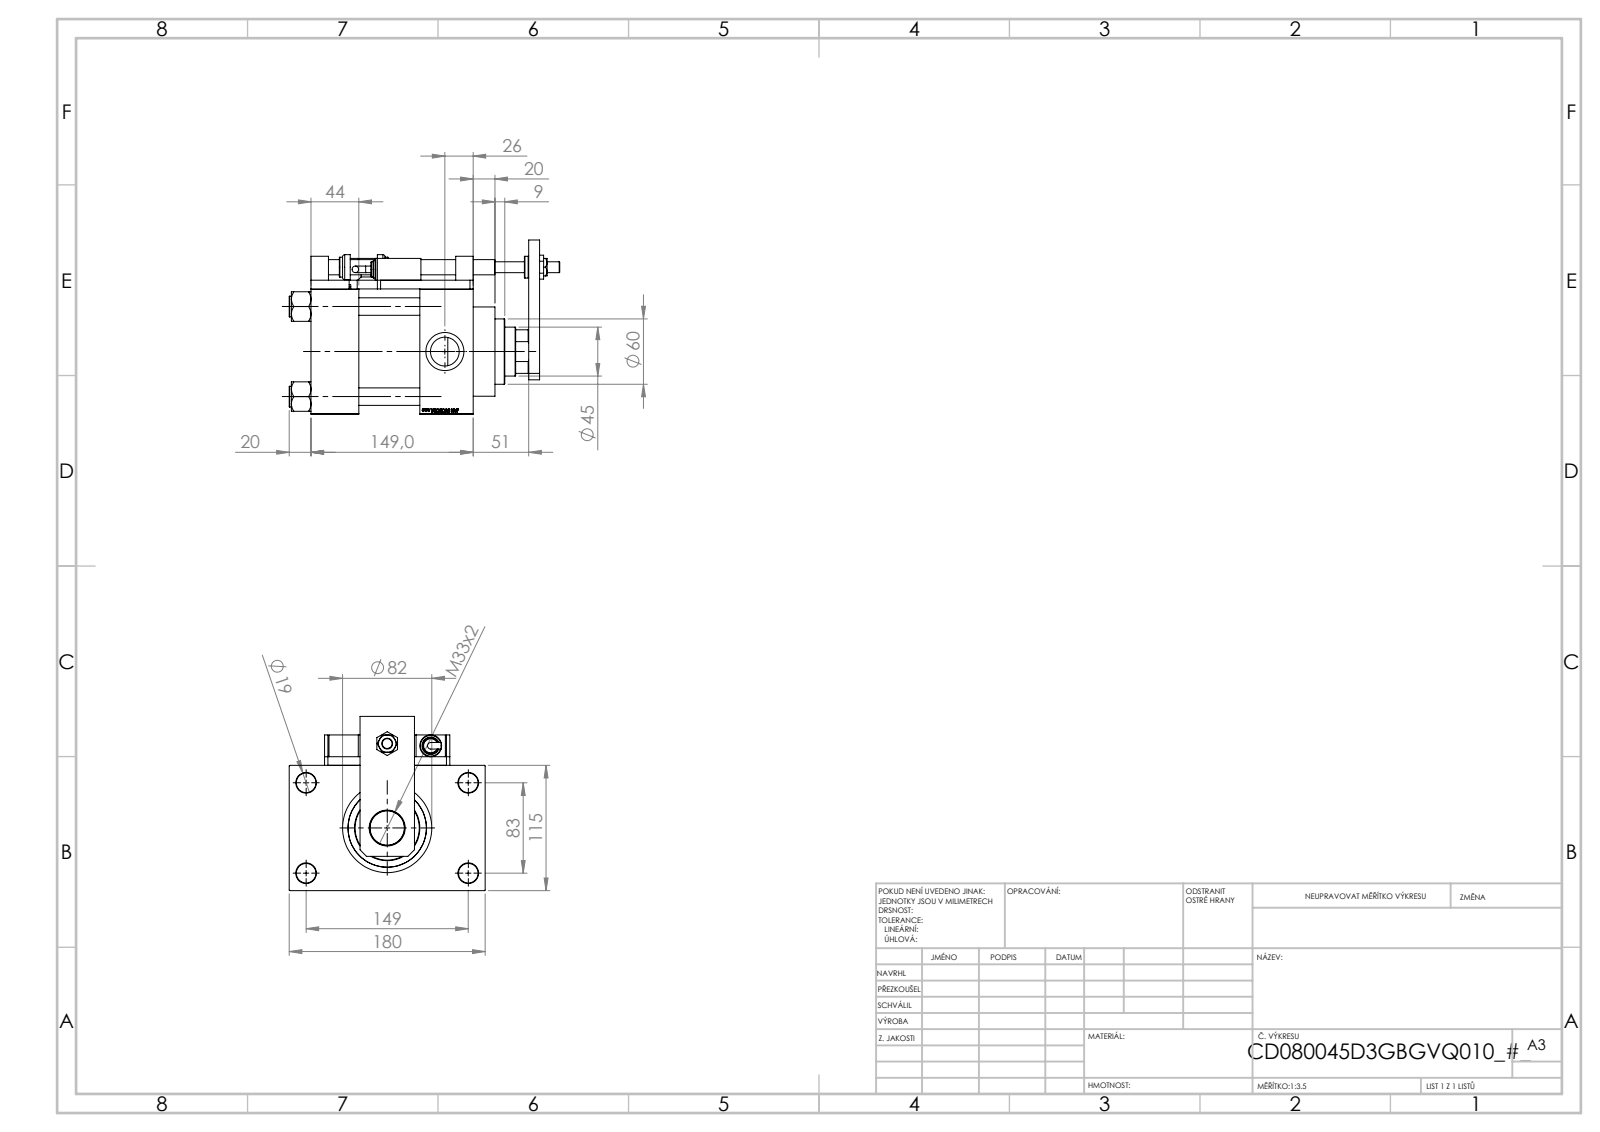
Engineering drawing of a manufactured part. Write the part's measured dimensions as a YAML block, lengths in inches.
part_name: "V215CD_VC_A; V215CD_SWITCH_Q_SWITCH; V215CD_SWITCH_Q_PODLOZKA_FRONT; Zatka_pro_OIL_PORT (+7 more)"
step_written_by: "SolidWorks 2019 (CONFIG_CONTROL_DESIGN)"
units: inches
bodies: {solids: 26, faces: 1480, planar: 714, cylindrical: 167, other: 599}
overall_size: [9.783, 7.087, 6.299]
volume: 137.2
surface_area: 605.7
round_holes:
  - {diameter: 0.335, count: 4}
  - {diameter: 0.531, count: 4}
  - {diameter: 0.63, count: 4}
  - {diameter: 0.709, count: 4}
  - {diameter: 1.041, count: 4}
  - {diameter: 1.378, count: 4}
  - {diameter: 0.276, count: 3}
  - {diameter: 0.394, count: 1}
  - {diameter: 0.551, count: 1}
  - {diameter: 1.24, count: 1}
  - {diameter: 1.299, count: 1}
  - {diameter: 1.772, count: 1}
round_bosses_or_shafts:
  - {diameter: 0.748, count: 4}
  - {diameter: 0.787, count: 3}
  - {diameter: 0.63, count: 2}
  - {diameter: 0.551, count: 2}
  - {diameter: 0.236, count: 2}
  - {diameter: 3.386, count: 1}
  - {diameter: 3.228, count: 1}
  - {diameter: 2.362, count: 1}
partial_cylinders:
  - {radius: 0.295, count: 4}
  - {radius: 0.866, count: 1}
face_to_face_distances: [4.528, 3.937, 0.315, 2.205, 5.866, 1.929, 1.732, 4.134, 4.843, 1.28]
hole_center_spacings: [1.305, 2.302, 3.256, 3.357, 3.513, 4.561, 5.607, 0.837]
